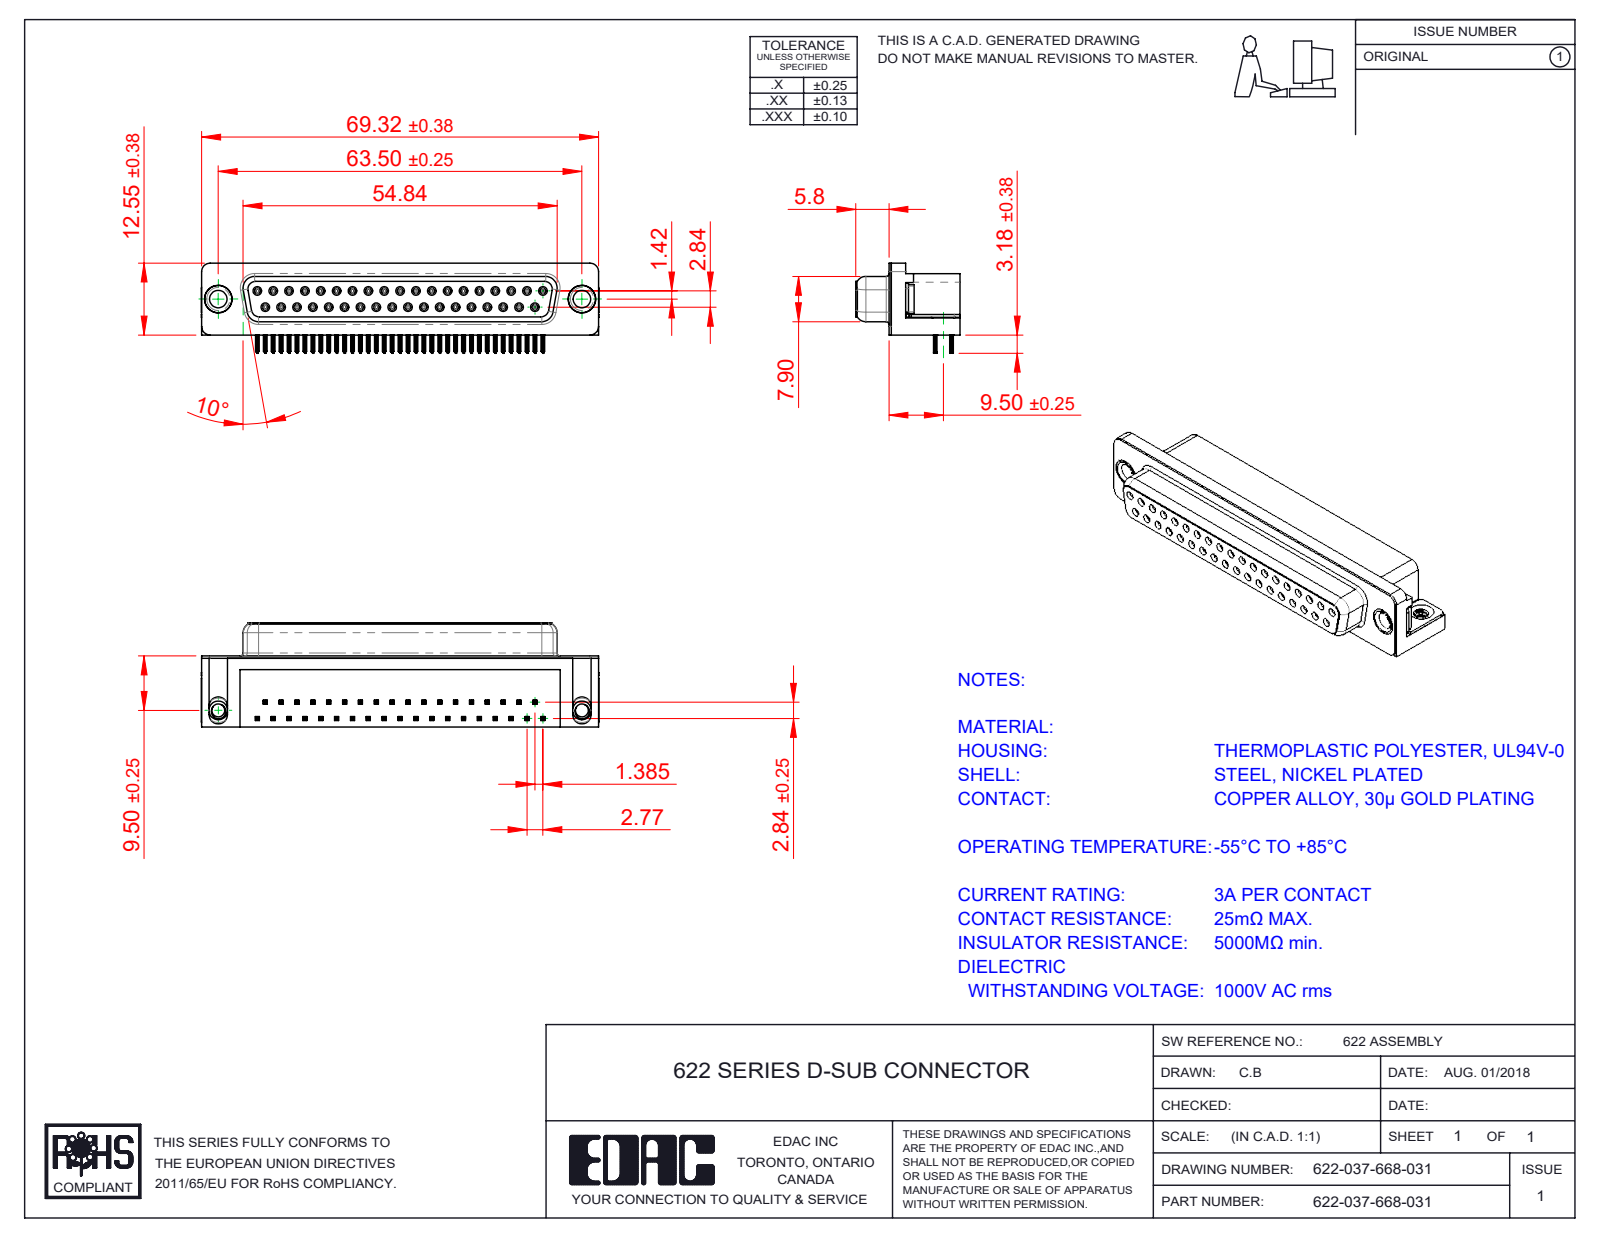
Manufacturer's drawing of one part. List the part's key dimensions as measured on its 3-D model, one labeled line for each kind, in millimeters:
Part name (STEP PRODUCT): 622 Housing_37 Socket; 622 Thru Hole Rivet; 622 2 Prong Board Lock; 622-037-668-031 (+3 more)
STEP written by: SolidWorks 2016 (CONFIG_CONTROL_DESIGN)
Units: millimetres
Bodies: 43 solids, 5562 faces (2536 planar, 1288 cylindrical, 1738 other)
Overall size (bounding box): 69.4 × 18.2 × 16.25
Volume: 10 442 mm³ · Surface area: 12 668 mm²
Round holes (diameter × count): ⌀0.8 ×37, ⌀0.9 ×37, ⌀3.05 ×2, ⌀4 ×2, ⌀4.8 ×2, ⌀5 ×2
Round bosses / shafts (diameter × count): ⌀1.2 ×37, ⌀4.9 ×2, ⌀4.75 ×2, ⌀3.85 ×2
Partial cylindrical surfaces — rounded edges, fillets, slot ends (radius × count): R0.1 ×296, R0.15 ×148, R0.35 ×74, R0.34 ×37, R0.28 ×18, R1 ×18, R0.5 ×10, R0.25 ×8
Main face-to-face distances: 0.4, 6.2, 12, 10.34, 0.45, 0.85, 6.65, 2.84, 1.32, 2.9
Hole centre spacings: 3.16, 2.77, 5.54, 8.31, 11.08, 22.16, 13.85, 19.39
